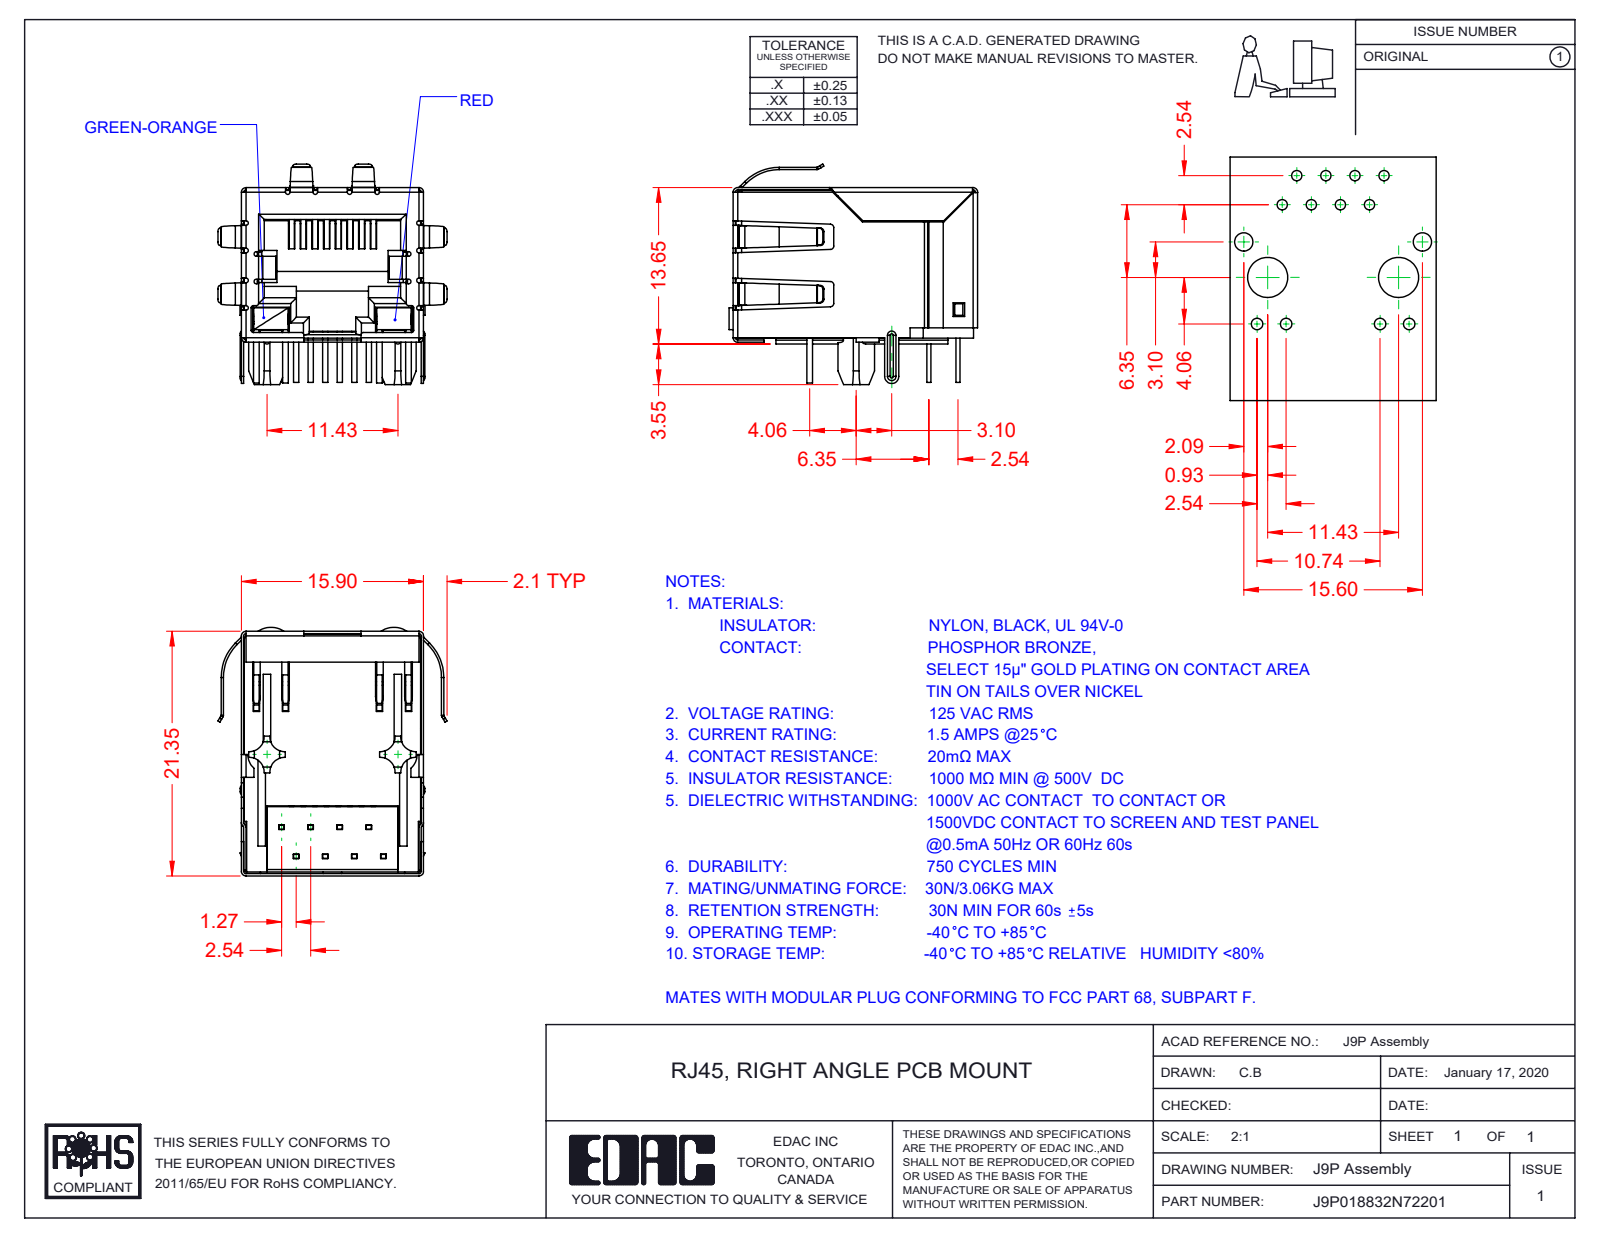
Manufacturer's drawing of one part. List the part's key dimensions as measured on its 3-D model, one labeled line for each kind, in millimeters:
Part name (STEP PRODUCT): J9P018832N72202; 9P-LED LED LH_7-Green-Orange; 9P-LED Insulator; 9P-LED Contact Lock (+4 more)
STEP written by: SolidWorks 2016 (CONFIG_CONTROL_DESIGN)
Units: millimetres
Bodies: 13 solids, 1474 faces (1042 planar, 338 cylindrical, 94 other)
Overall size (bounding box): 21.7 × 20 × 19.25
Volume: 2 687 mm³ · Surface area: 7 515 mm²
Partial cylindrical surfaces — rounded edges, fillets, slot ends (radius × count): R0.2 ×39, R0.5 ×22, R0.3 ×20, R0.4 ×16, R1.3 ×8, R0.23 ×5, R0.11 ×4, R0.31 ×4
Main face-to-face distances: 15.45, 15.7, 15.65, 0.35, 0.54, 15.5, 12.36, 0.6, 1.4, 0.59
